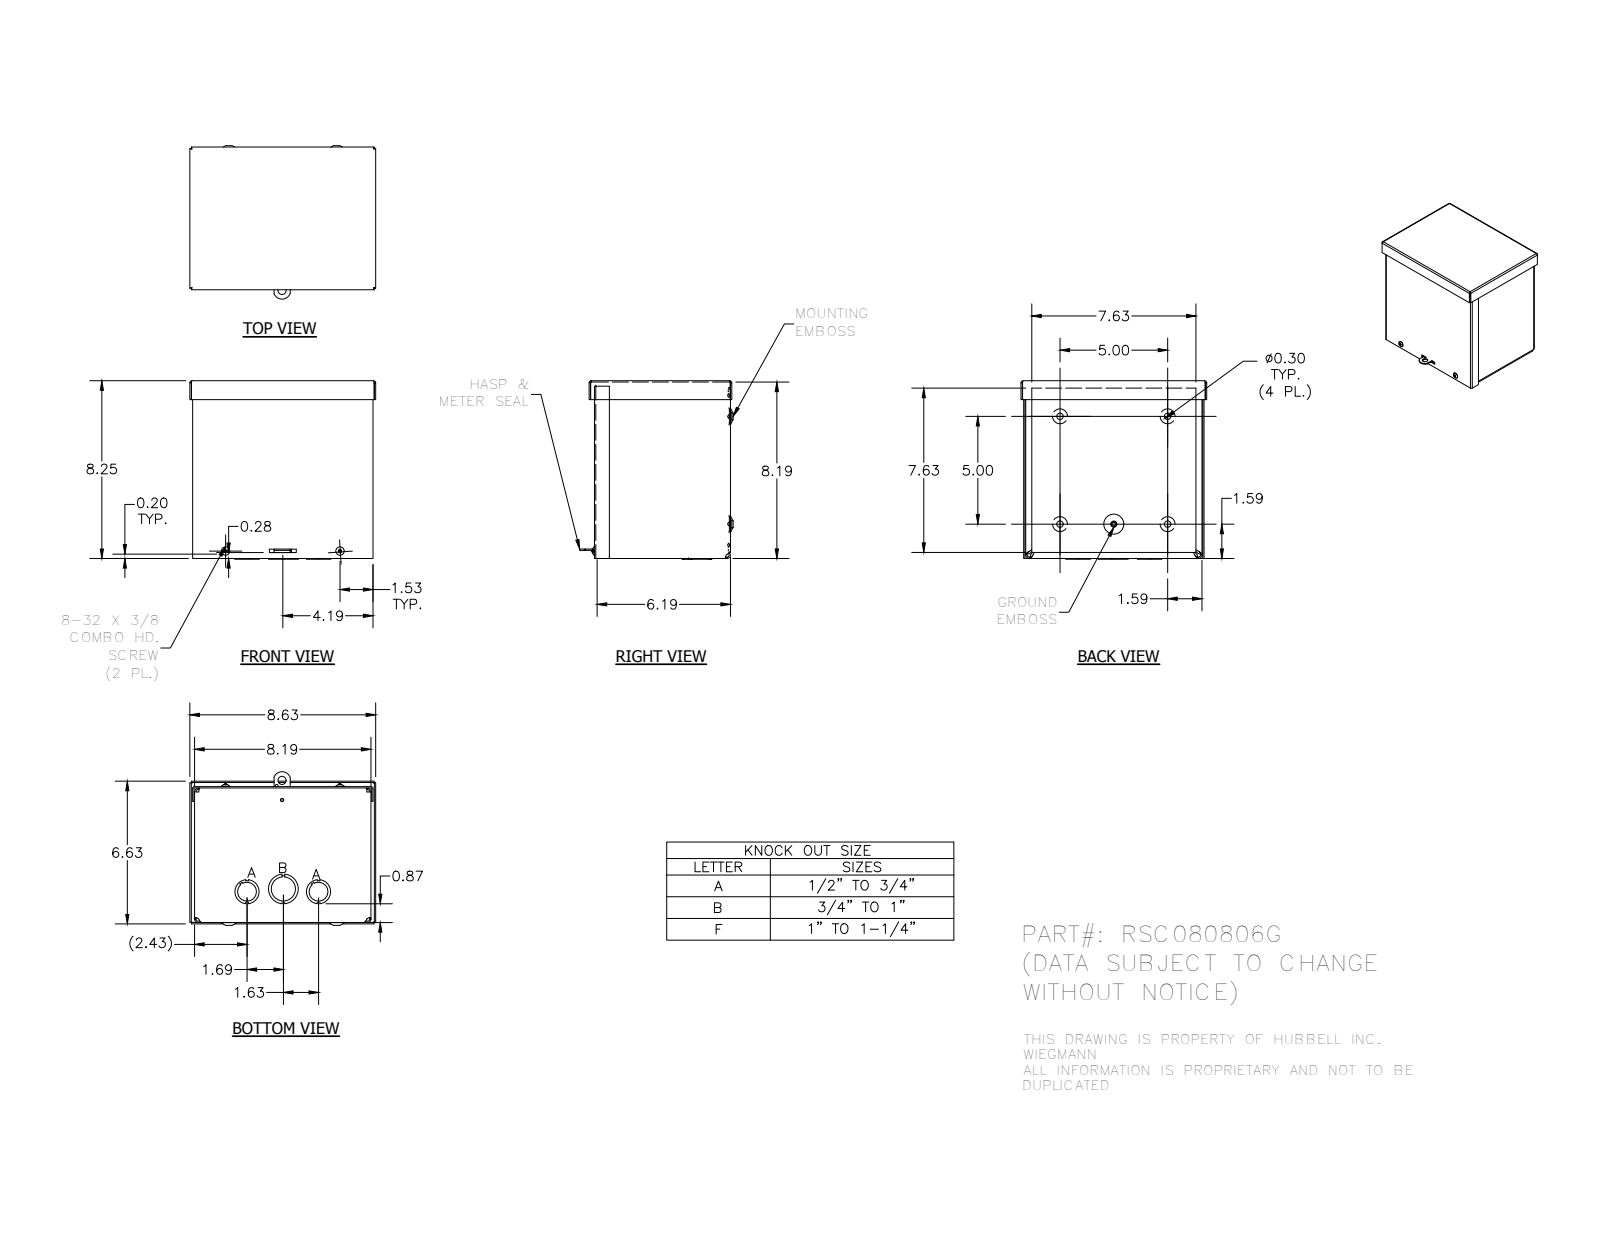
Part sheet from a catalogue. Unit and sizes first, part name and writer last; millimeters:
Units: millimetres
Overall size (bounding box): 219.07 × 210.32 × 180.97
Round holes (diameter × count): ⌀7.62 ×4, ⌀7.95 ×4, ⌀28.57 ×3, ⌀3.17 ×2, ⌀3.76 ×2, ⌀22.22 ×2, ⌀3.96 ×1, ⌀4.19 ×1, ⌀9.52 ×1, ⌀34.92 ×1
Round bosses / shafts (diameter × count): ⌀9.75 ×2, ⌀4.17 ×2, ⌀5.8 ×1
Partial cylindrical surfaces — rounded edges, fillets, slot ends (radius × count): R0.25 ×10, R0.79 ×8, R2.37 ×8, R3.17 ×8, R4.75 ×8, R0.53 ×4, R0.79 ×4, R1.4 ×4
Main face-to-face distances: 1.58, 206.39, 1.57, 207.97, 158.73, 3.15, 157.15, 1.59, 160.32, 158.74
Hole centre spacings: 127, 27.24, 32.03, 63.5, 134.95, 141.98, 154, 158.83
Volume: 467 854 mm³ · Surface area: 603 254 mm²
Bodies: 7 solids, 503 faces (238 planar, 121 cylindrical, 144 other)
Part name (STEP PRODUCT): RSC080806G_WRAP; RSC0808G_LID; RSC0806G_CAP; 3183 (+4 more)
STEP written by: Autodesk Inventor 2014 (AUTOMOTIVE_DESIGN)
